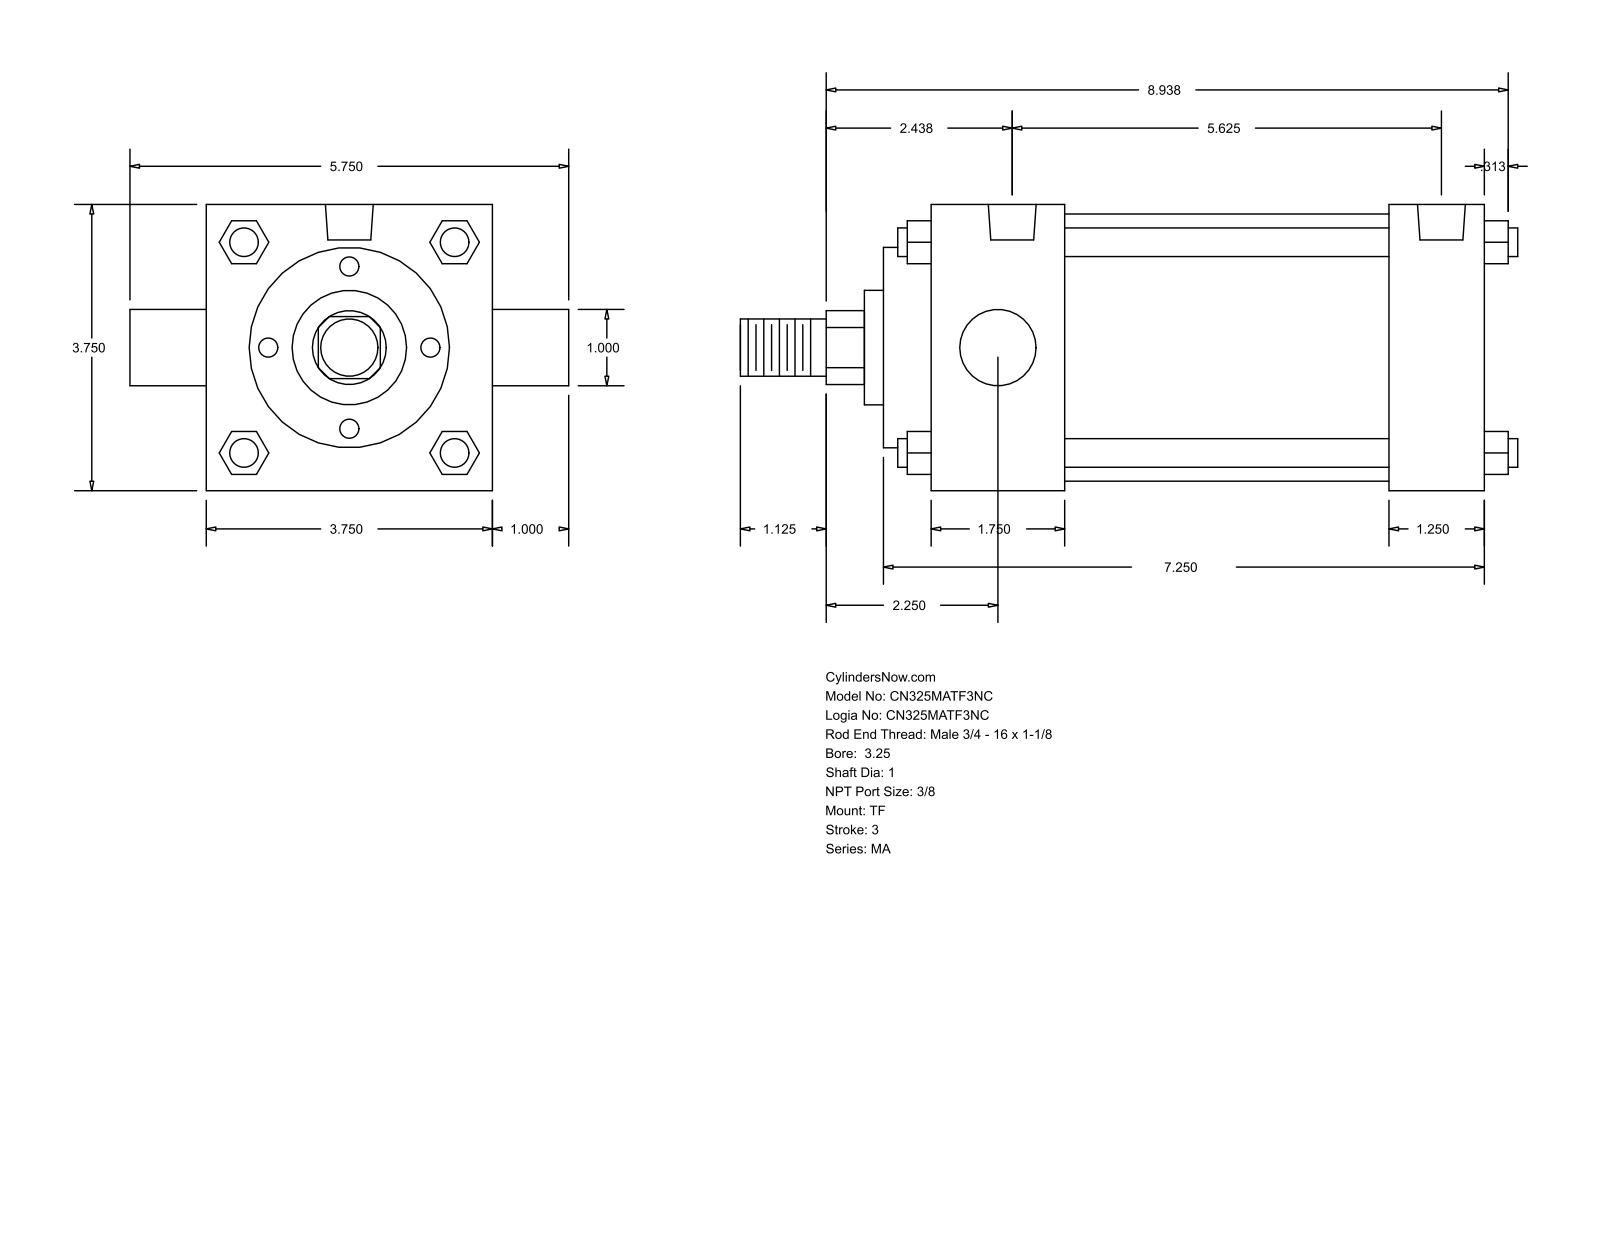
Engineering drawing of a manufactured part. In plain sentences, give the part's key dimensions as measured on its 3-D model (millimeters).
The part is named "MA_TF__0325_1". Its 3-D file was written by "GSSL Pune (CONFIG_CONTROL_DESIGN)". It is 0 solids with 122 faces: 93 planar, 29 cylindrical and 0 other. Overall it measures 258.76 by 146.05 by 95.25 millimeters. Round holes: 3 of diameter 11.11, 2 of diameter 15.93. Round bosses or shafts: 4 of diameter 9.53, 2 of diameter 25.4, 1 of diameter 88.9, 1 of diameter 66.67, 1 of diameter 38.1, 1 of diameter 19.05. Partial cylindrical surfaces (rounded edges, fillets, slot ends): 1 of radius 12.29. The main face-to-face distances are 95.24, 184.15, 200.02, 44.46, 152.4, 107.94, 139.69, 31.75, 15.87, 60.33. The hole center spacings are 4.76, 138.12, 133.36, 142.88.
